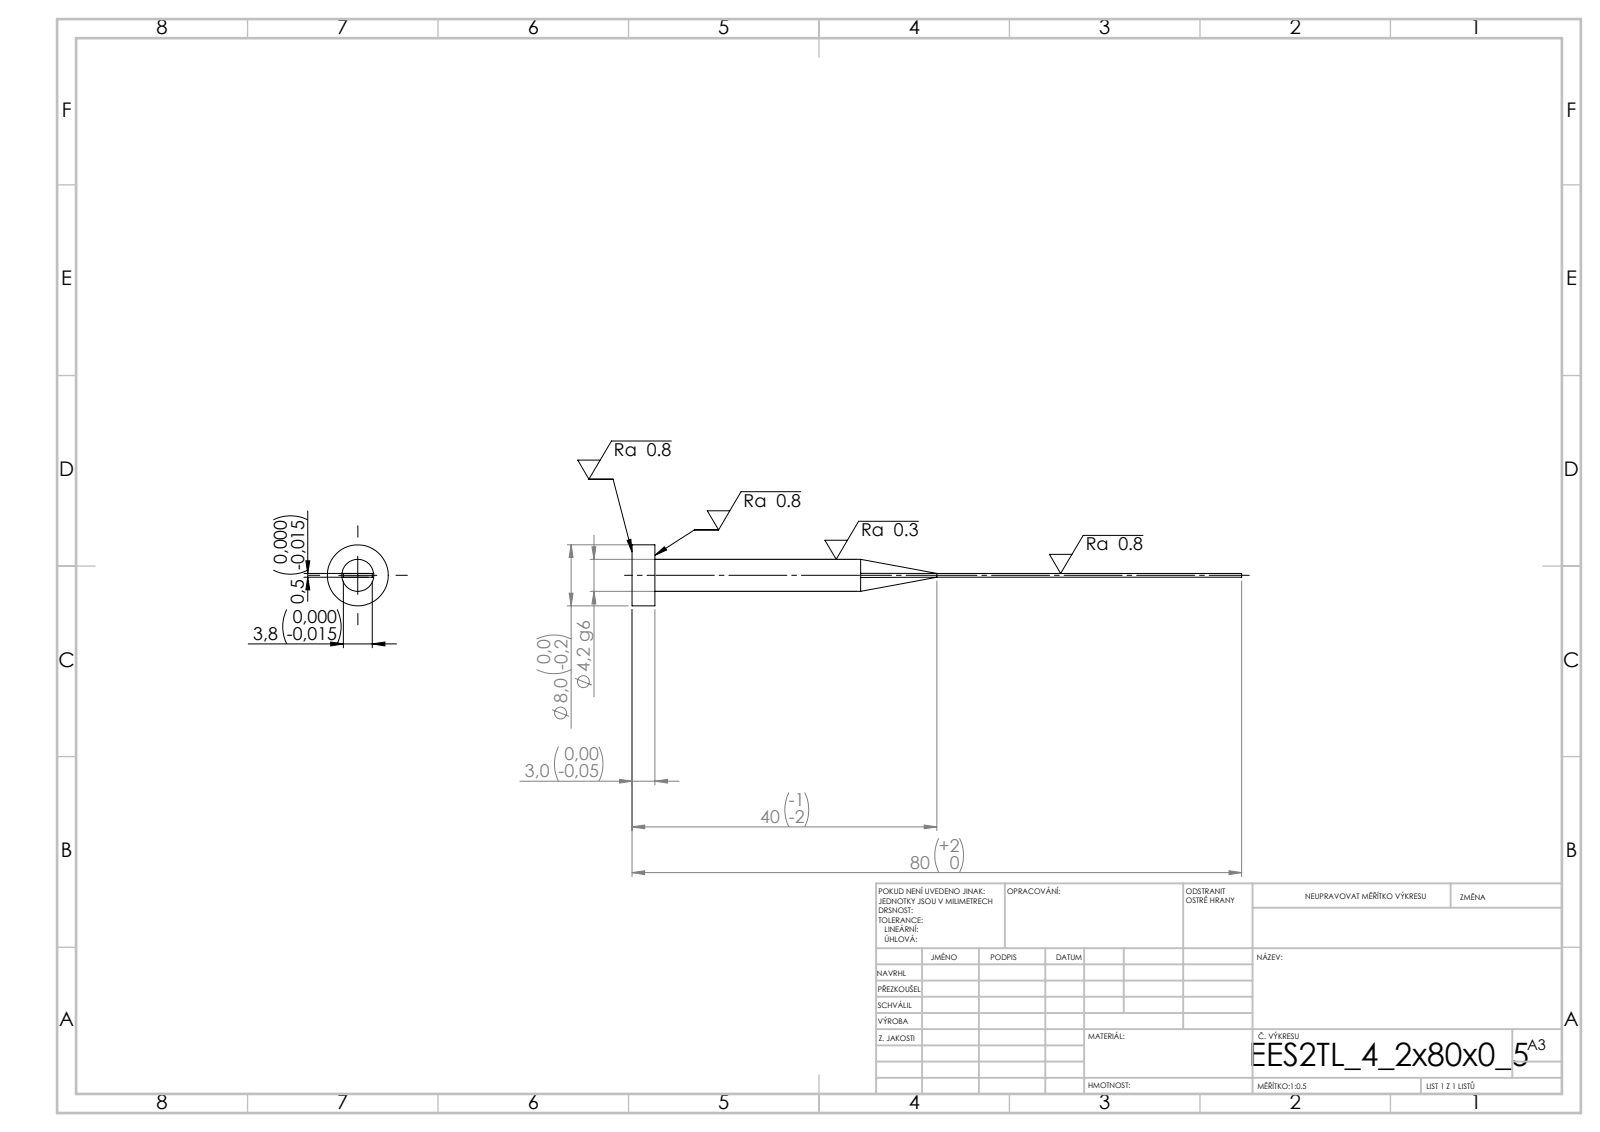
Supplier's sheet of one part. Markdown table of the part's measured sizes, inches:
| quantity | value |
| --- | --- |
| STEP written by | SolidWorks 2019 (CONFIG_CONTROL_DESIGN) |
| units | inches |
| bodies | 1 solid, 15 faces (7 planar, 4 cylindrical, 4 other) |
| overall size | 3.15 × 0.315 × 0.315 |
| volume | 0.041 in³ |
| surface area | 1.5 in² |
| round bosses / shafts (diameter × count) | 0.315 × 1, 0.165 × 1 |
| main face-to-face distances | 0.02, 0.118, 0.15, 3.15, 3.031 |
